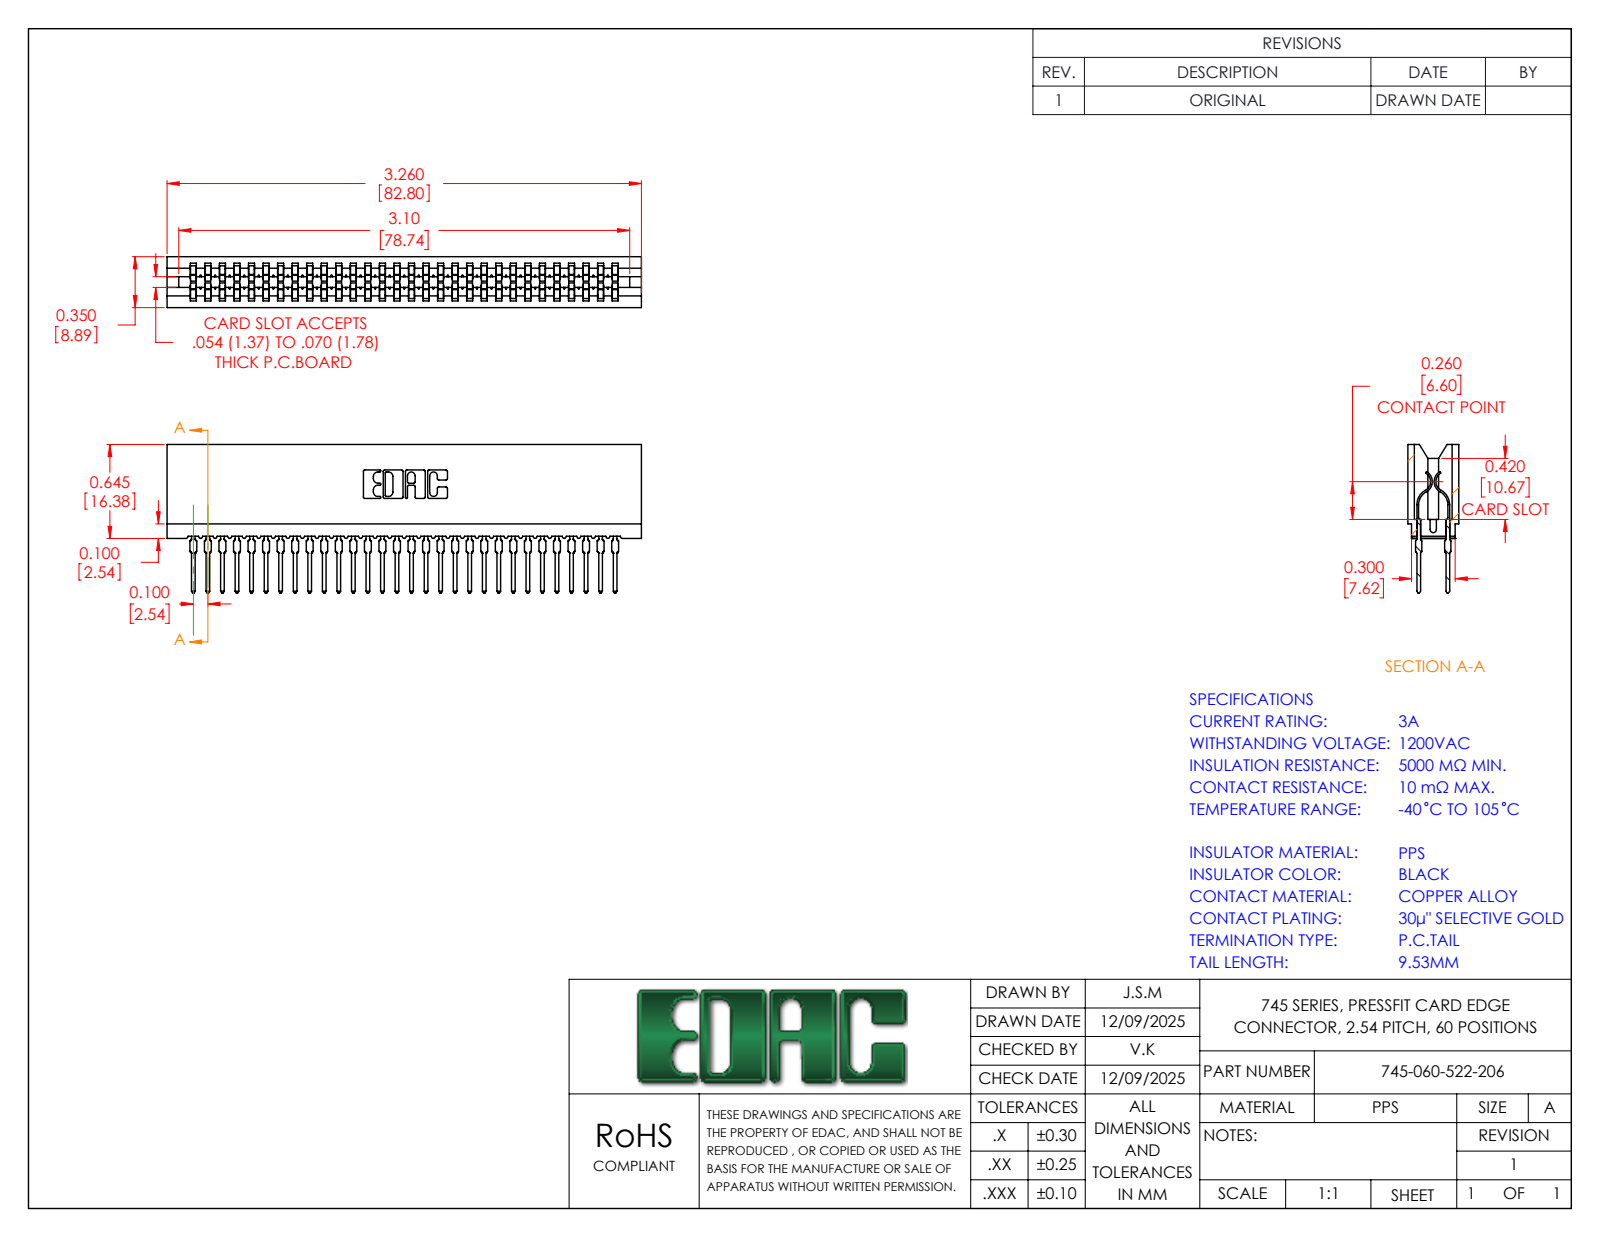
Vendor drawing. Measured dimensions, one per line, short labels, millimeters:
name: 745-060-522-206; 745 Part_Insulator Option - 06; 745-292-001_522
written by: SolidWorks 2023 (CONFIG_CONTROL_DESIGN)
unit: mm
bodies: 61 solids, 5466 faces (2816 planar, 1090 cylindrical, 1560 other)
size: 82.8 × 25.92 × 8.89
volume: 7 571 mm³; area: 15 348 mm²
rounds: 120× R0.55, 60× R0.38, 22× R0.25, 8× R0.13, 8× R0.28, 6× R0.17, 6× R0.8, 3× R0.67
face distances: 5.08, 2.54, 8.89, 1.59, 7.3, 3.51, 5.38, 1.92, 3.79, 1.14
